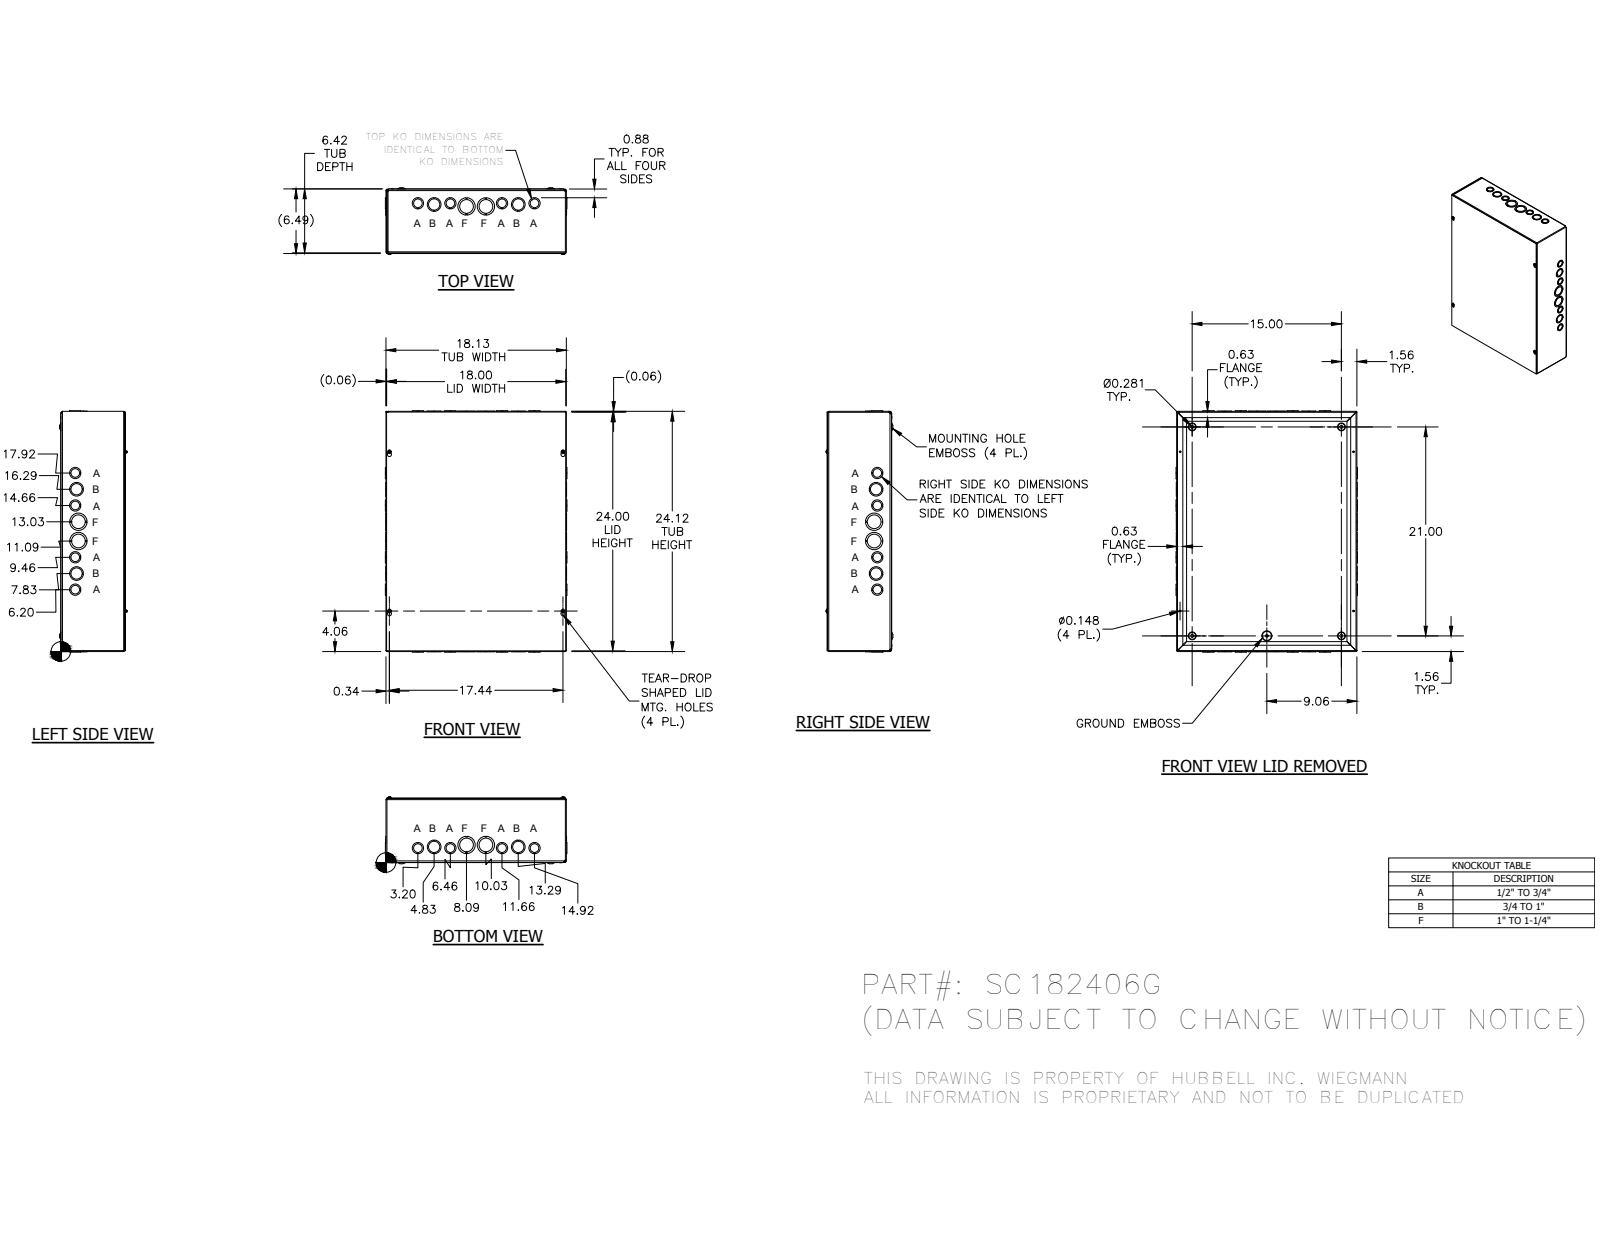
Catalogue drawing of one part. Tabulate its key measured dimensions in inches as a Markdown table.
| quantity | value |
| --- | --- |
| part name | SC1824GBKP; SC182406GWRA; SC1824GLID; 34056 (+1 more) |
| STEP written by | Autodesk Inventor 2014 (AUTOMOTIVE_DESIGN) |
| units | inches |
| bodies | 38 solids, 1255 faces (839 planar, 273 cylindrical, 143 other) |
| overall size | 24.249 × 18.249 × 6.716 |
| round holes (diameter × count) | 1.125 × 12, 0.875 × 8, 1.375 × 8, 0.148 × 4, 0.3 × 4, 1.75 × 4, 0.165 × 1 |
| round bosses / shafts (diameter × count) | 0.18 × 8, 0.384 × 4, 0.164 × 4, 0.228 × 1 |
| partial cylindrical surfaces (radius × count) | 0.031 × 8, 0.093 × 8, 0.055 × 4, 0.062 × 4, 0.094 × 4, 0.11 × 4, 0.117 × 4, 0.124 × 4 |
| main face-to-face distances | 0.074, 6.417, 6.343, 0.062, 6.491, 18.063, 0.062, 18.125, 18.001, 24.125 |
| hole center spacings | 1.635, 1.659, 3.265, 3.584, 5.204, 6.831, 8.46, 18.54 |
